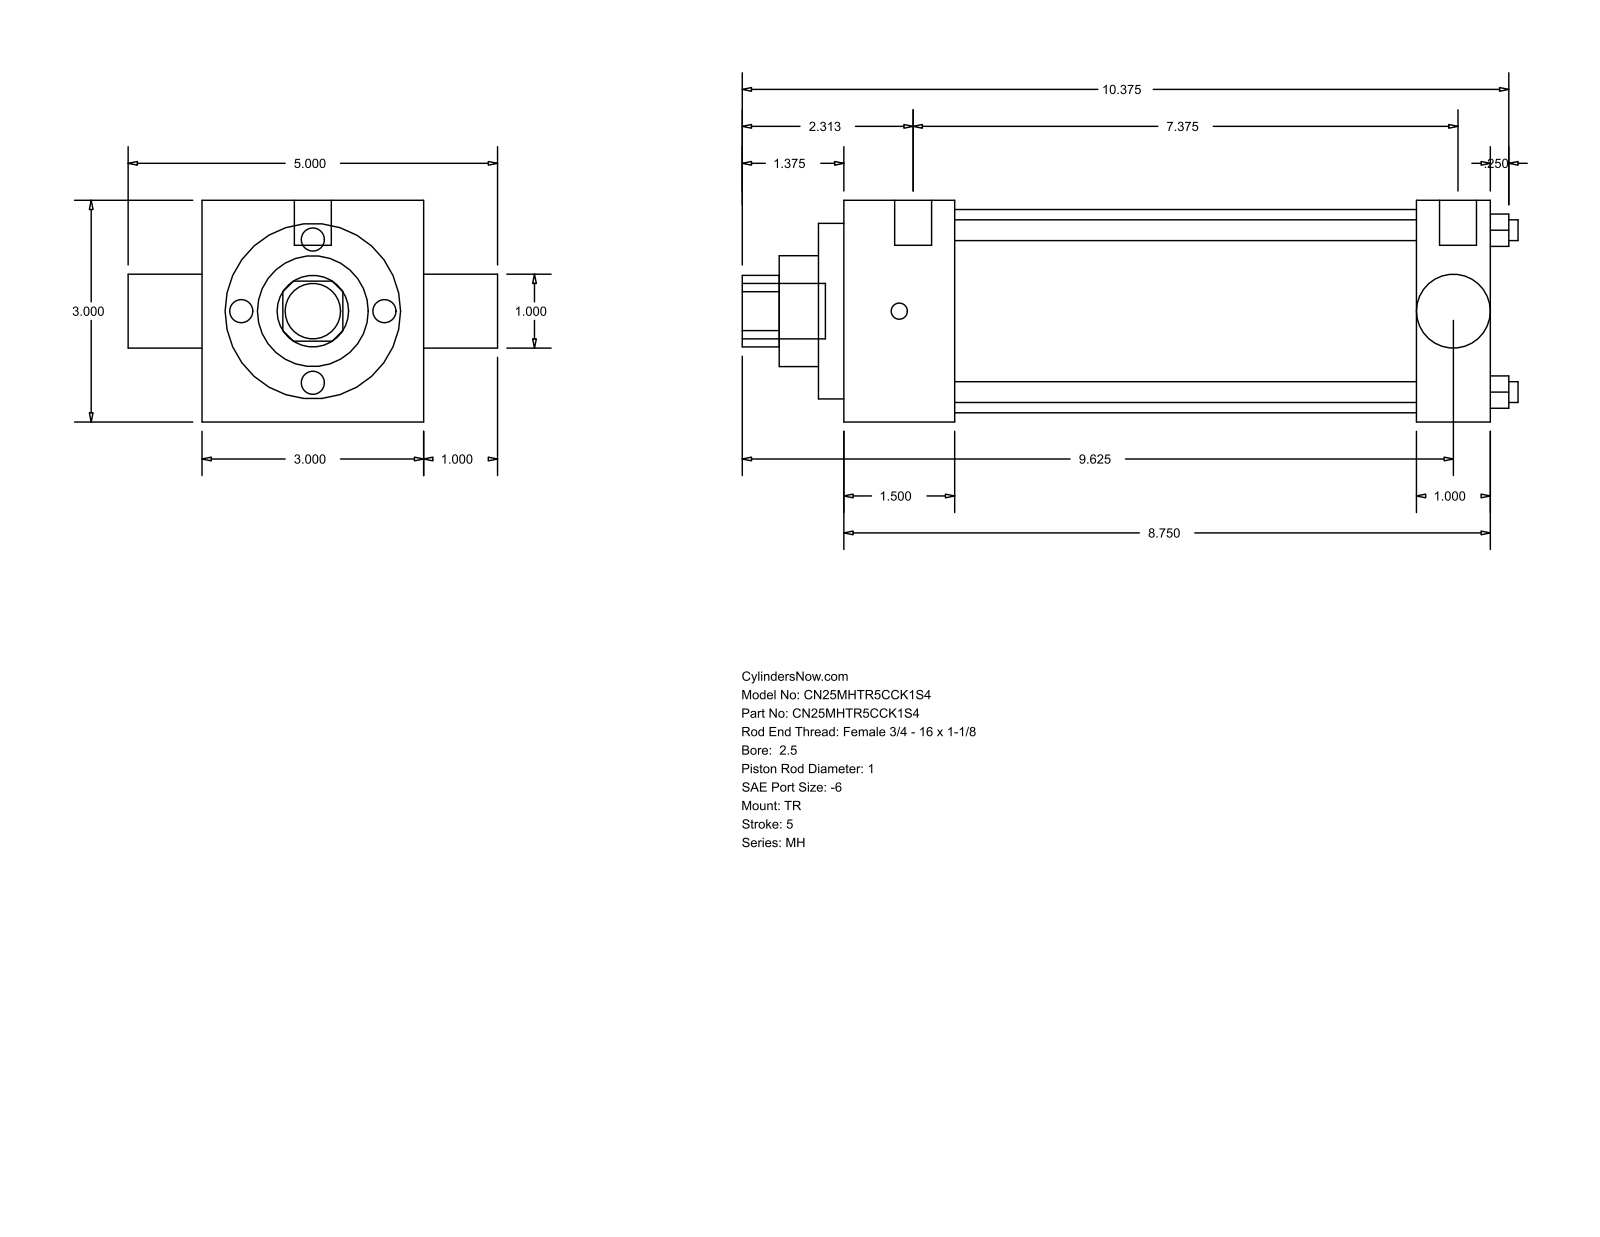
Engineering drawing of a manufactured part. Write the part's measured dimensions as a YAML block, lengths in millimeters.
part_name: "MH_TR__0250_1"
step_written_by: "GSSL Pune (CONFIG_CONTROL_DESIGN)"
units: millimeters
bodies: {solids: 0, faces: 86, planar: 61, cylindrical: 25, other: 0}
overall_size: [266.7, 127, 76.2]
round_holes:
  - {diameter: 7.14, count: 4}
  - {diameter: 25.35, count: 1}
  - {diameter: 25.4, count: 1}
  - {diameter: 38.1, count: 1}
  - {diameter: 60.33, count: 1}
  - {diameter: 69.85, count: 1}
round_bosses_or_shafts:
  - {diameter: 5.56, count: 3}
  - {diameter: 12.7, count: 2}
  - {diameter: 19.05, count: 1}
partial_cylinders:
  - {radius: 12.29, count: 1}
face_to_face_distances: [76.2, 222.26, 25.4, 38.11, 184.15, 196.86, 158.75, 8.73, 46.84, 205.59]
hole_center_spacings: [39.33, 55.62, 78.66]
